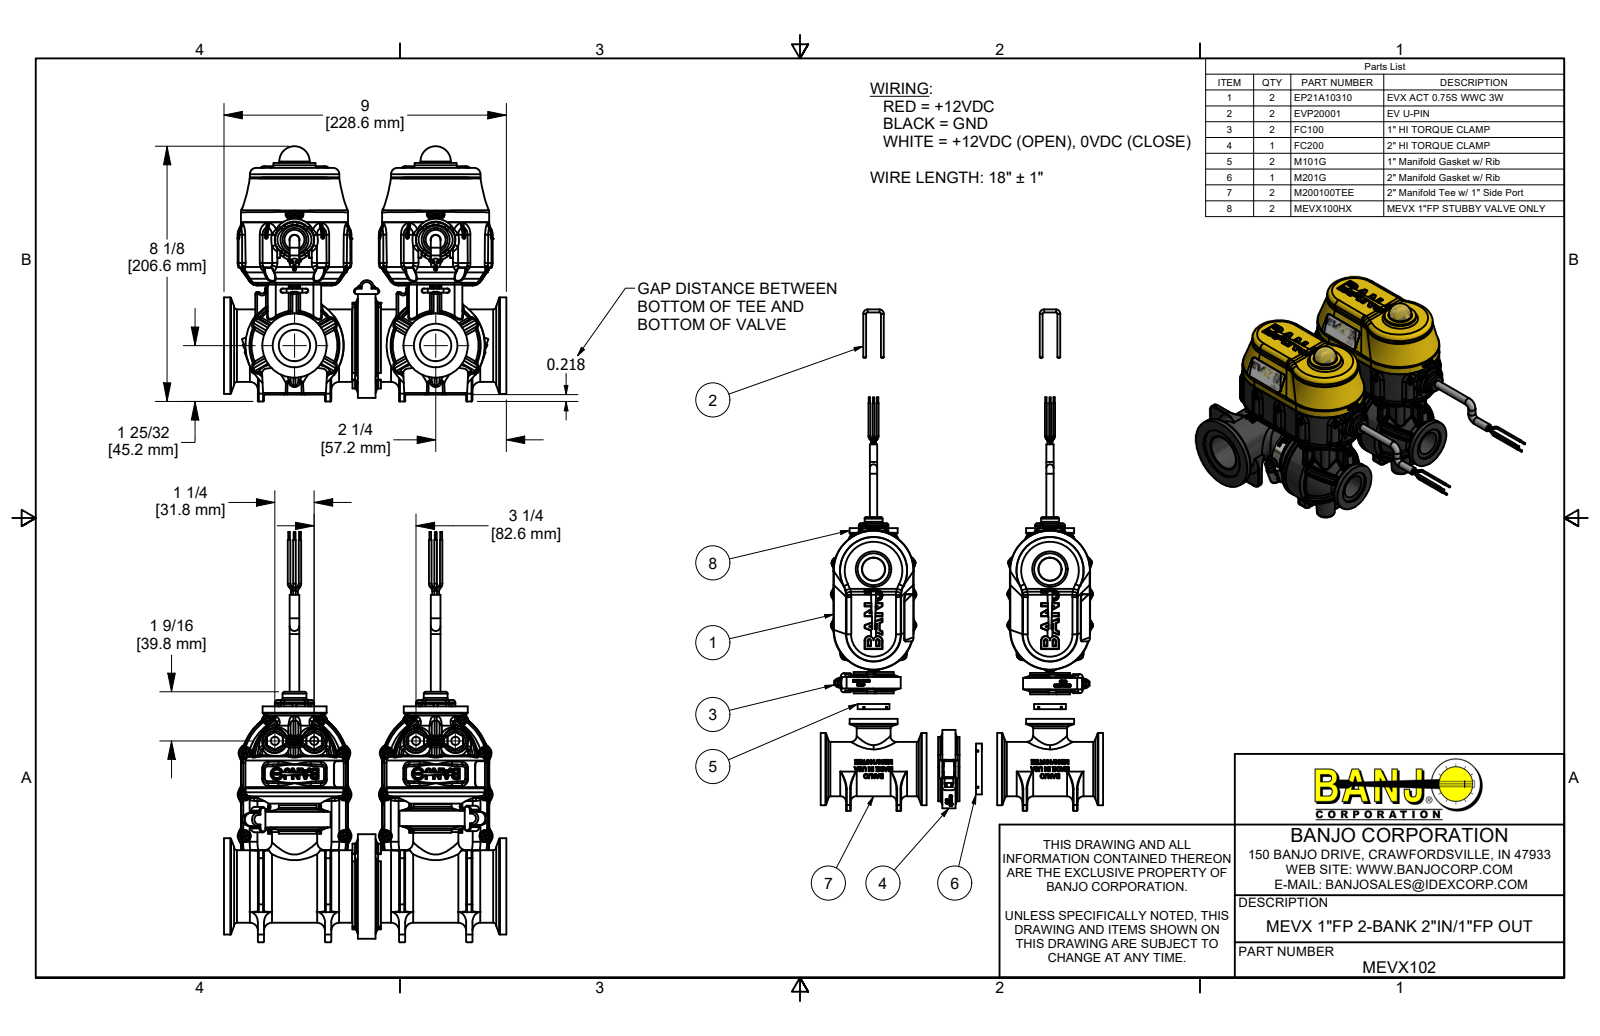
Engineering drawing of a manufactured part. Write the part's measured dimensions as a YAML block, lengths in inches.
part_name: "MEVX102; EP21A10310; EP10310; IRF4905 (+8 more)"
step_written_by: "Autodesk Inventor 2019 (AUTOMOTIVE_DESIGN)"
units: inches
bodies: {solids: 176, faces: 24049, planar: 6816, cylindrical: 6572, other: 10661}
overall_size: [13.07, 9, 8.133]
volume: 123.1
surface_area: 1343
round_holes:
  - {diameter: 0.095, count: 22}
  - {diameter: 0.15, count: 22}
  - {diameter: 0.08, count: 14}
  - {diameter: 0.107, count: 8}
  - {diameter: 0.126, count: 8}
  - {diameter: 0.136, count: 8}
  - {diameter: 0.148, count: 8}
  - {diameter: 0.15, count: 8}
  - {diameter: 0.17, count: 8}
  - {diameter: 0.135, count: 6}
  - {diameter: 0.25, count: 5}
  - {diameter: 0.105, count: 4}
round_bosses_or_shafts:
  - {diameter: 0.25, count: 34}
  - {diameter: 0.08, count: 30}
  - {diameter: 0.14, count: 22}
  - {diameter: 0.108, count: 22}
  - {diameter: 0.085, count: 22}
  - {diameter: 0.058, count: 12}
  - {diameter: 0.27, count: 8}
  - {diameter: 0.219, count: 8}
partial_cylinders:
  - {radius: 0.013, count: 360}
  - {radius: 0.04, count: 290}
  - {radius: 0.01, count: 177}
  - {radius: 0.02, count: 122}
  - {radius: 0.03, count: 117}
  - {radius: 0.005, count: 94}
  - {radius: 0.06, count: 93}
  - {radius: 0.125, count: 60}
face_to_face_distances: [0.1, 4.5, 2.565, 0.06, 0.151, 0.211, 0.995, 3.505, 1.896, 1.836]
hole_center_spacings: [4.5, 1.79, 1.662, 2.656, 2.69, 2.715, 2.913, 4.406]
